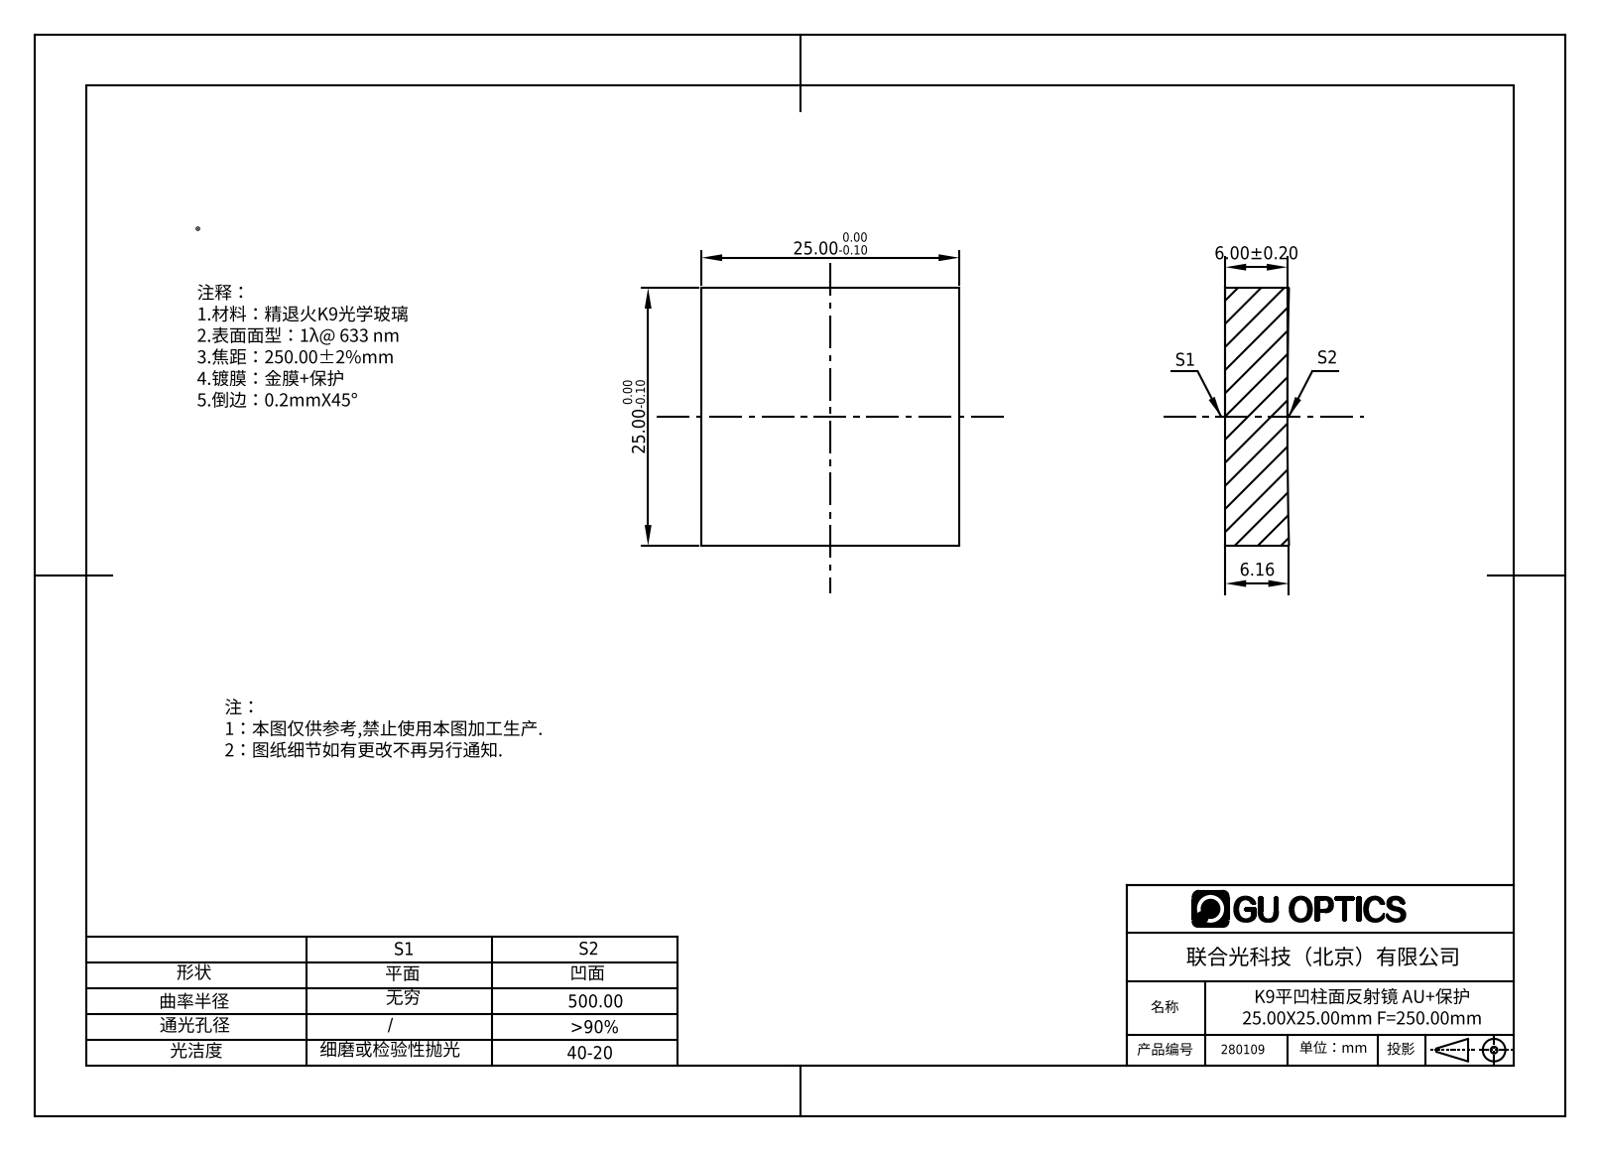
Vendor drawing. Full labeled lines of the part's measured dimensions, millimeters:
Part name (STEP PRODUCT): 280021
STEP written by: SolidWorks 2016 (AUTOMOTIVE_DESIGN)
Units: millimetres
Bodies: 1 solid, 7 faces (5 planar, 2 cylindrical, 0 other)
Overall size (bounding box): 25 × 25 × 6.16
Volume: 3 783 mm³ · Surface area: 1 860 mm²
Partial cylindrical surfaces — rounded edges, fillets, slot ends (radius × count): R500 ×1
Main face-to-face distances: 25
